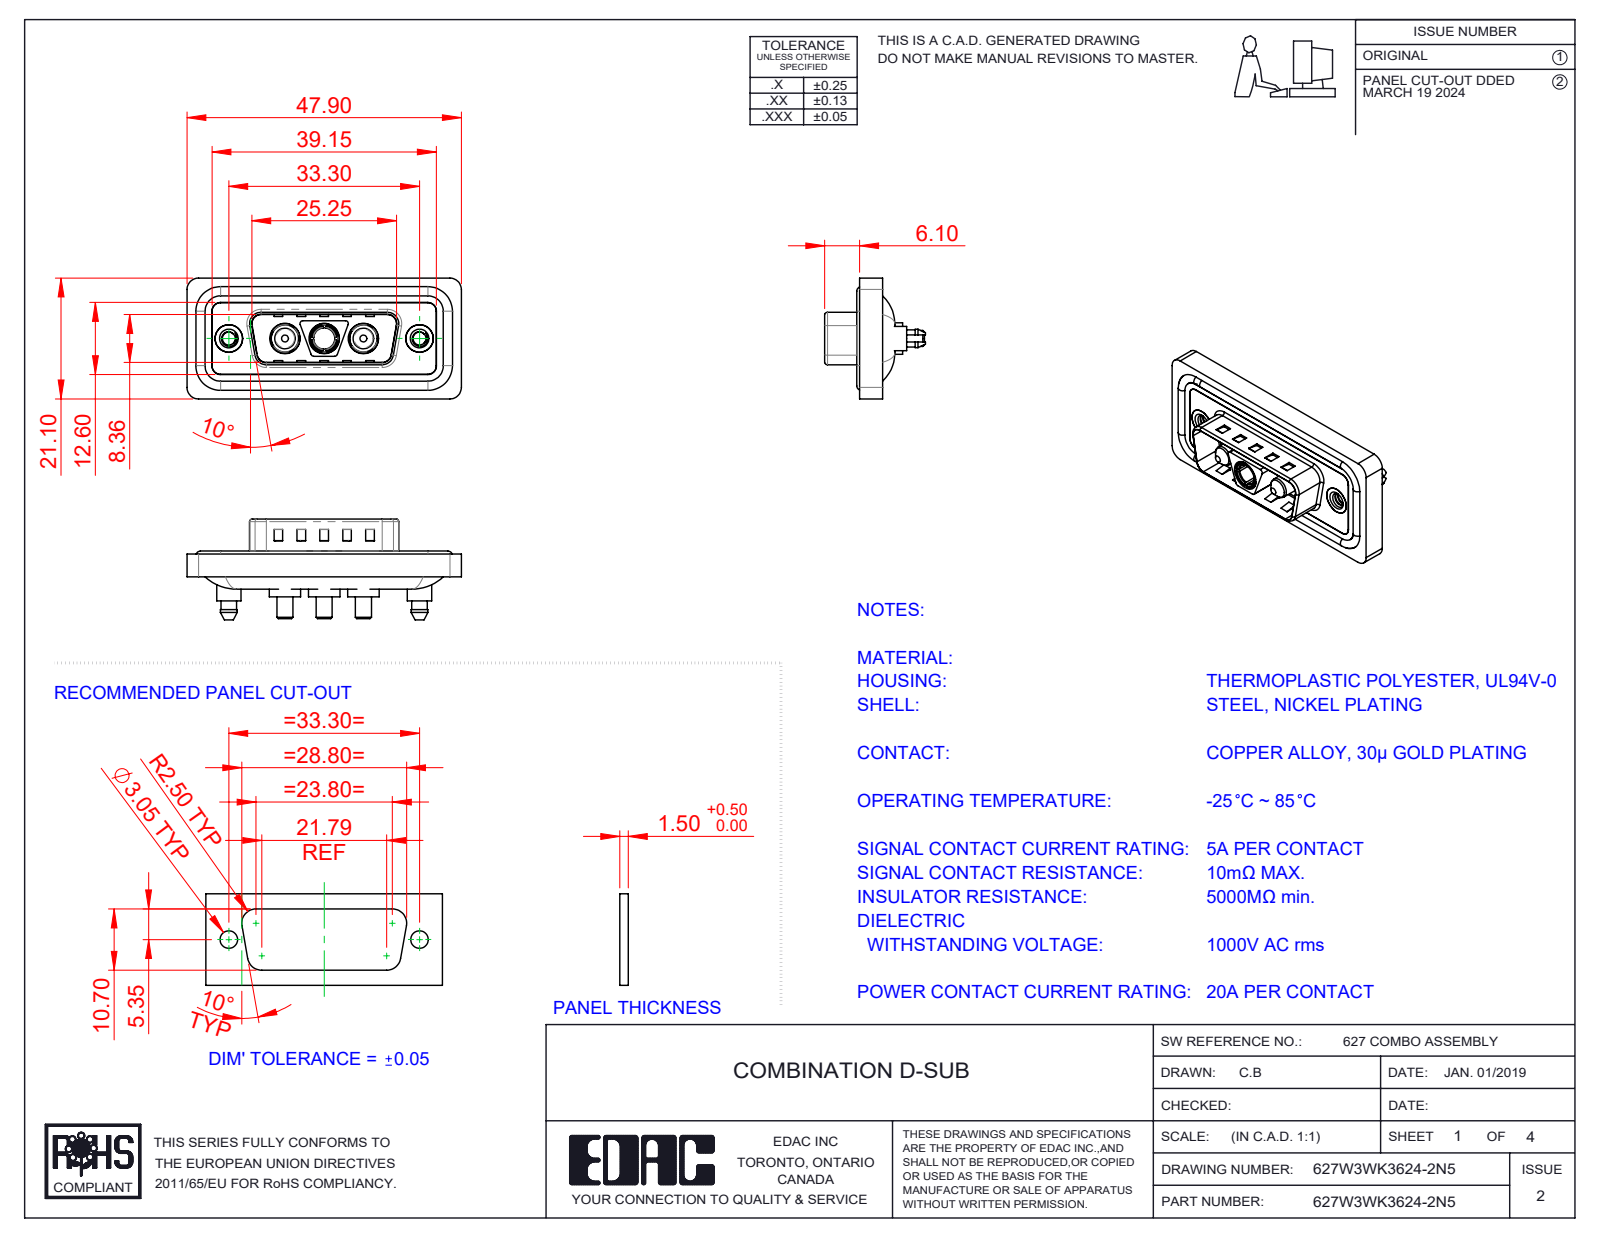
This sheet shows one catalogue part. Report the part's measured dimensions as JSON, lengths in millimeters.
{"part_name": "627Combo Threaded Boardlock_5; Power Socket_20A S; 627Combo Housing_3WK3; 627W3WK3624-2N5 (+4 more)", "step_written_by": "SolidWorks 2023 (CONFIG_CONTROL_DESIGN)", "units": "millimeters", "bodies": {"solids": 13, "faces": 659, "planar": 247, "cylindrical": 282, "other": 130}, "overall_size": [47.9, 21.1, 17.6], "volume_mm3": 5822, "surface_area_mm2": 9460, "round_holes": [[4.85, 3], [5.3, 3], [2.26, 2], [4, 2], [4.8, 2], [5, 2], [3.7, 1]], "round_bosses_or_shafts": [[1.6, 4], [5.5, 3], [5.2, 3], [4.75, 3], [3.75, 3], [2.8, 3], [5.4, 2], [4.9, 2]], "partial_cylinders_radius": [[1.5, 28], [2, 20], [0.5, 12], [1.6, 10], [0.25, 4], [0.6, 4], [0.65, 4], [0.9, 4]], "face_to_face_distances": [0.4, 1.1, 1.5, 0.5, 1.6, 3.1, 2.9, 4, 0.7, 0.82], "hole_center_spacings": [6.85, 9.8, 16.65, 23.5, 13.7, 33.3]}
